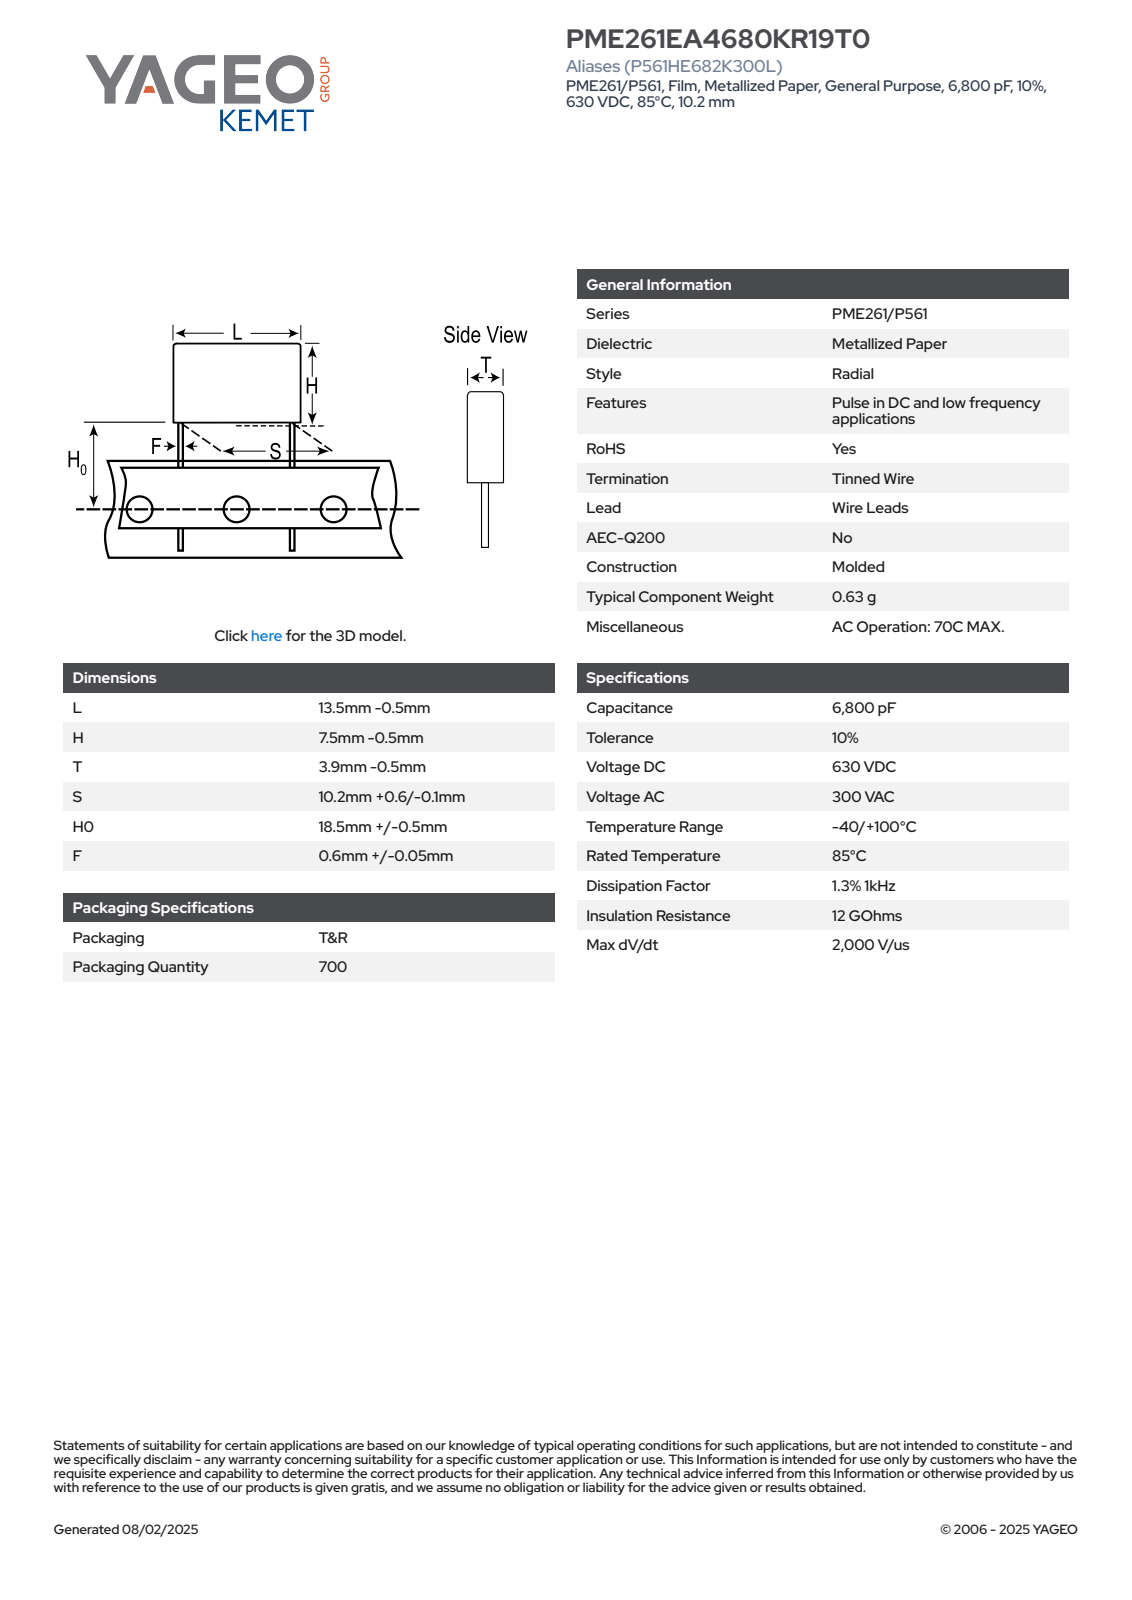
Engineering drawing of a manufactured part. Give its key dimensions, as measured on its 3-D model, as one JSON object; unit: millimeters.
{"part_name": "CFR_MOLDED_13.5X7.5X3.9_L13H7T3.4S10.2H019F0.65", "step_written_by": "SolidWorks 2014 (AUTOMOTIVE_DESIGN)", "units": "millimeters", "bodies": {"solids": 4, "faces": 73, "planar": 65, "cylindrical": 8, "other": 0}, "overall_size": [26, 13, 3.4], "volume_mm3": 320, "surface_area_mm2": 397, "round_bosses_or_shafts": [[0.65, 2]], "partial_cylinders_radius": [[0.5, 4]], "face_to_face_distances": [3.4, 7, 13, 19, 26, 2.94, 23.1, 4.1, 2.9, 21.94]}
